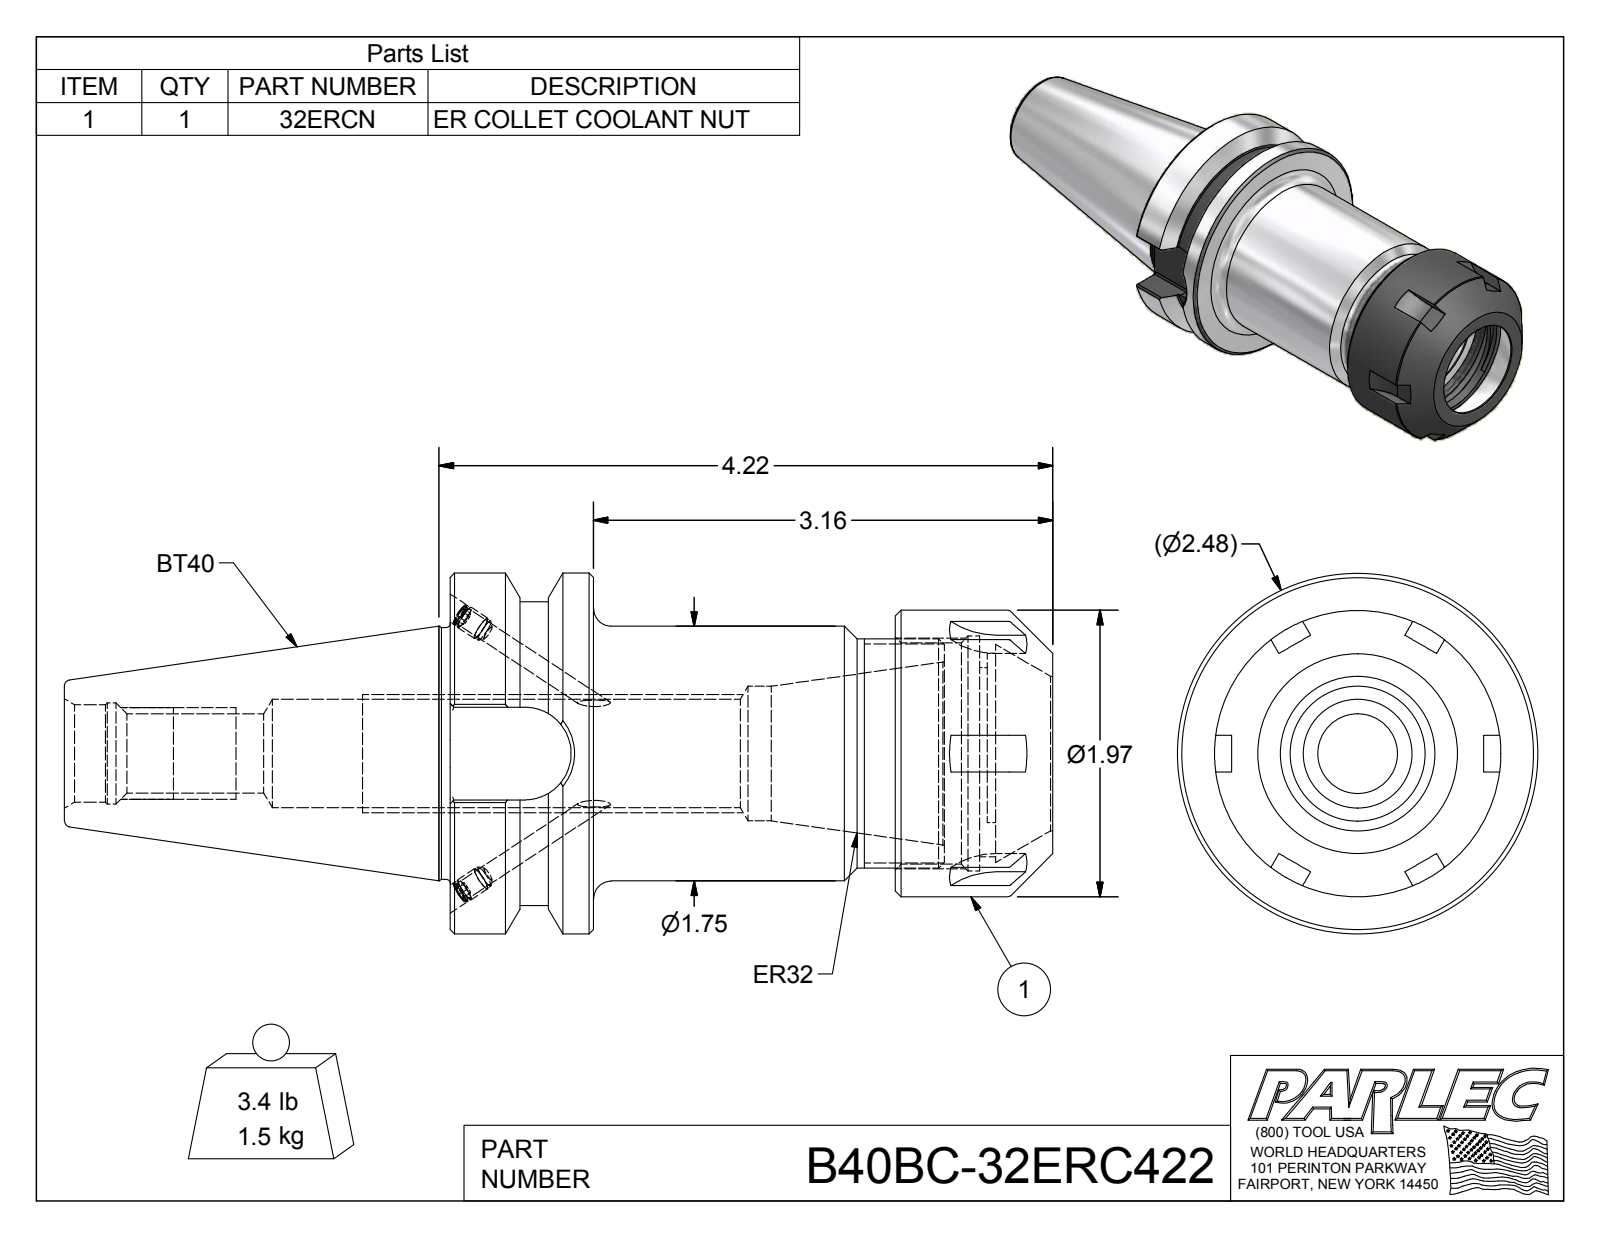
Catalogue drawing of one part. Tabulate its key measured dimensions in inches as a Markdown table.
| quantity | value |
| --- | --- |
| part name | B40BC-32ERC422; B40BCB-32ER4-1; 029-965; 32ERCN |
| STEP written by | Autodesk Inventor 2012 (AUTOMOTIVE_DESIGN) |
| units | inches |
| bodies | 4 solids, 155 faces (68 planar, 45 cylindrical, 42 other) |
| overall size | 6.795 × 2.48 × 2.48 |
| volume | 11.87 in³ |
| surface area | 71.17 in² |
| round holes (diameter × count) | 0.13 × 2, 0.161 × 2, 0.545 × 1, 0.67 × 1, 0.694 × 1, 0.745 × 1, 0.925 × 1, 1.063 × 1, 1.299 × 1, 1.522 × 1, 1.614 × 1 |
| round bosses / shafts (diameter × count) | 0.165 × 2, 0.157 × 2, 2.48 × 1, 2.087 × 1, 1.969 × 1, 1.75 × 1, 1.73 × 1, 1.575 × 1 |
| partial cylindrical surfaces (radius × count) | 0.02 × 8, 0.5 × 6, 0.319 × 1, 0.689 × 1 |
| main face-to-face distances | 0.984, 3.059, 2.076, 3.638, 2.654, 0.579, 4.142, 3.158, 1.083, 0.504 |
| hole center spacings | 0.059 |
